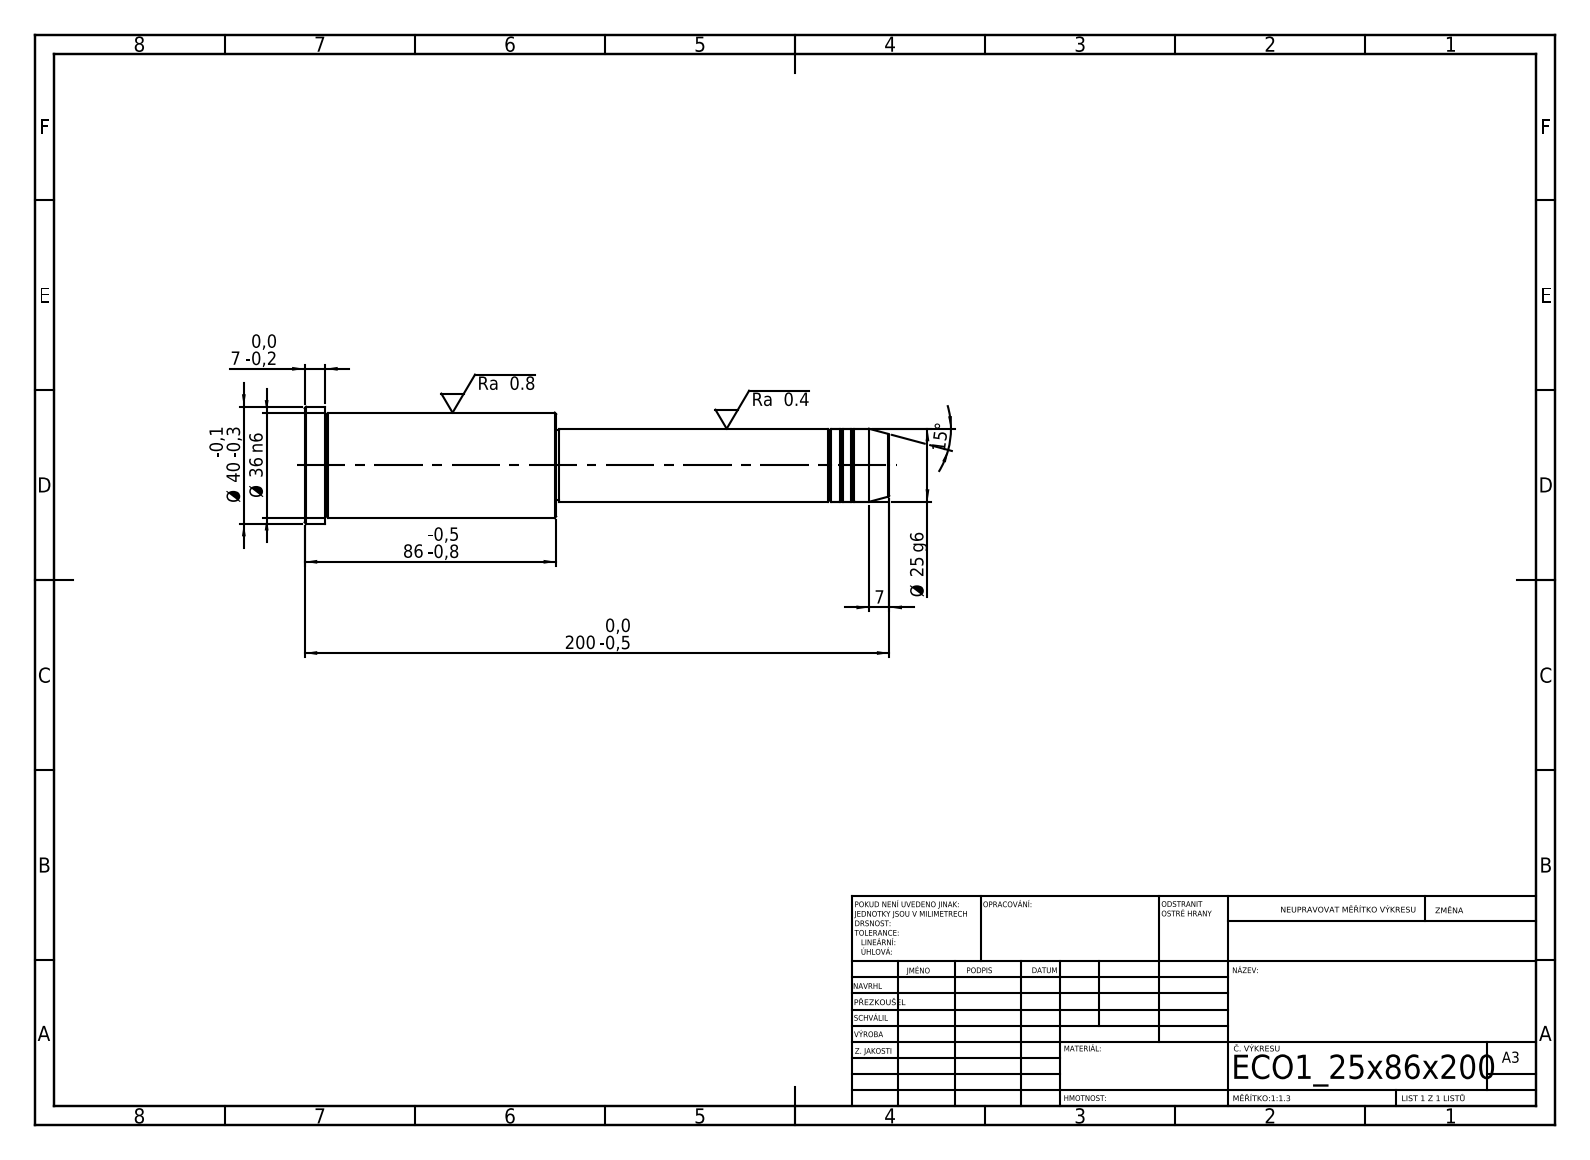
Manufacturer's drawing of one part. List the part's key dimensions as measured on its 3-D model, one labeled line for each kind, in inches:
STEP written by: SolidWorks 2019 (CONFIG_CONTROL_DESIGN)
Units: inches
Bodies: 1 solid, 43 faces (5 planar, 14 cylindrical, 24 other)
Overall size (bounding box): 7.874 × 1.575 × 1.575
Volume: 8.816 in³ · Surface area: 33.02 in²
Round bosses / shafts (diameter × count): ⌀1.575 ×1, ⌀1.417 ×1, ⌀0.984 ×1, ⌀0.945 ×1
Main face-to-face distances: 3.386, 4.488, 7.874, 7.598, 3.11, 0.276, 4.449, 0.039, 3.15, 3.425
